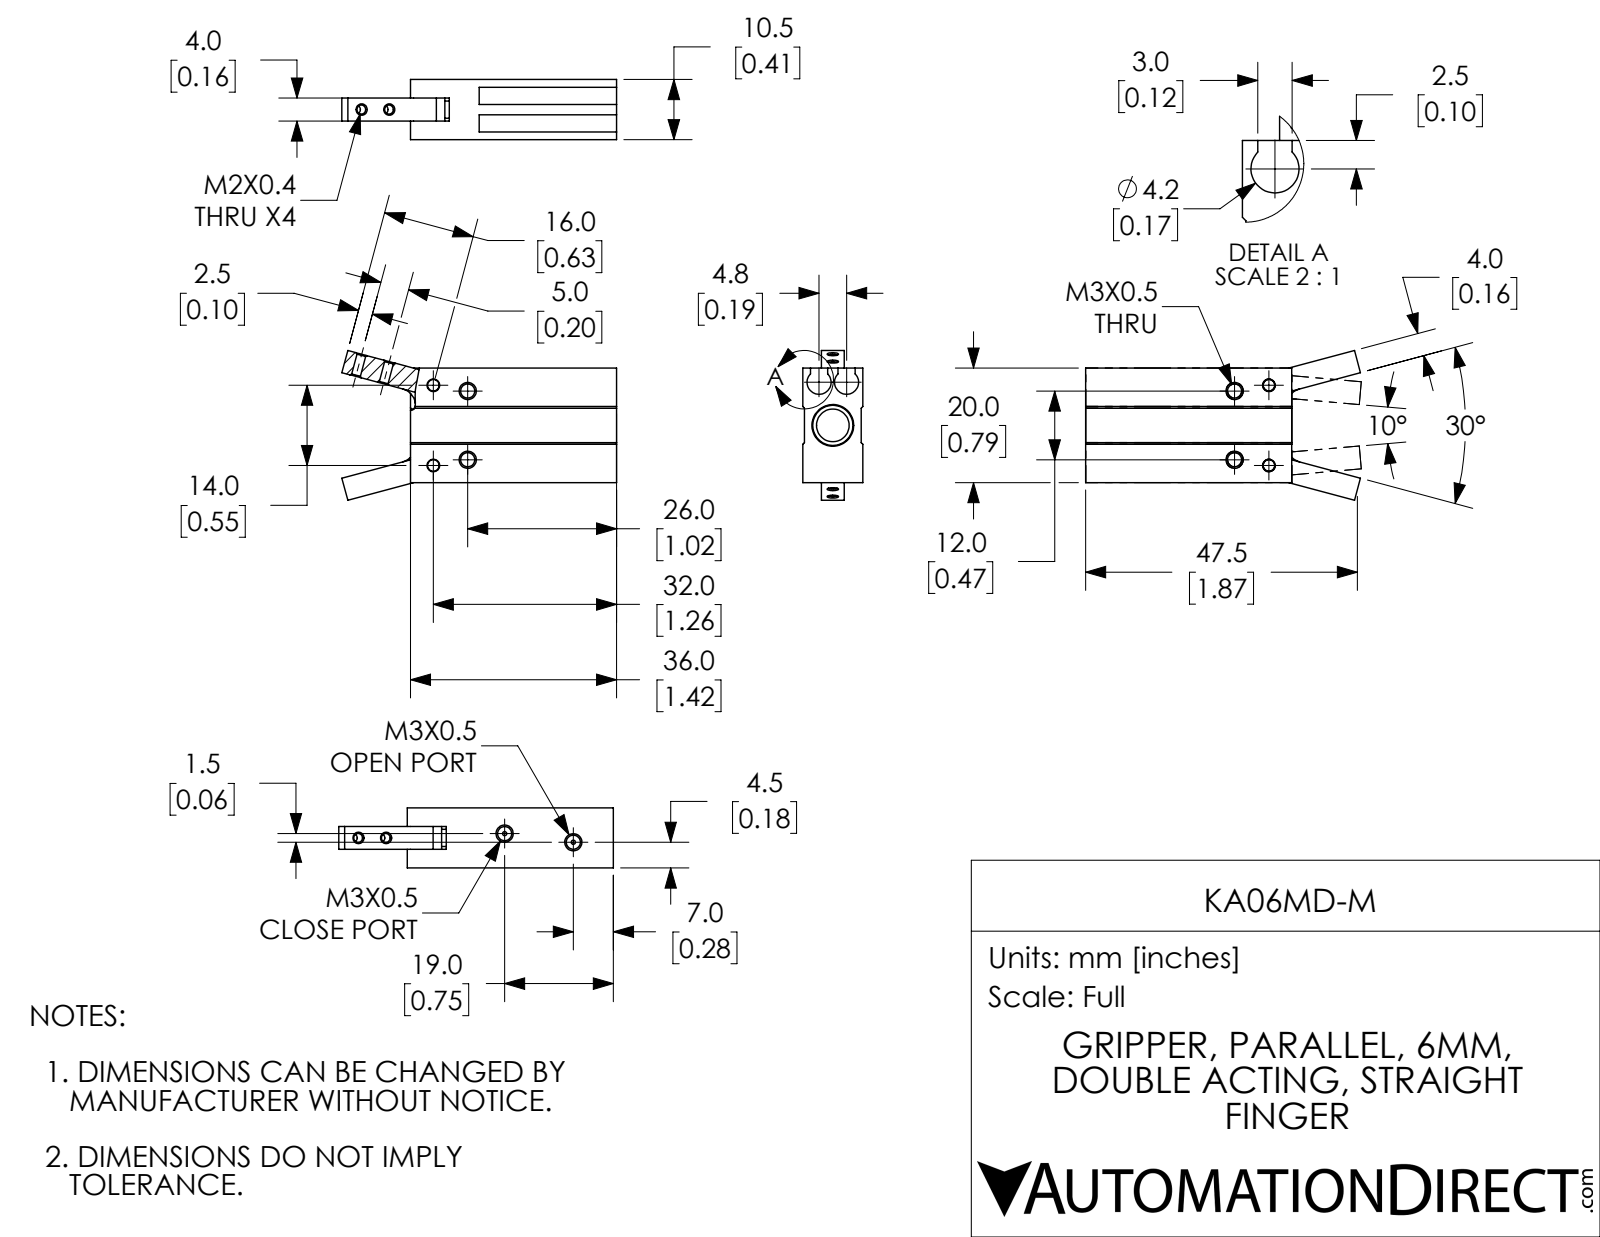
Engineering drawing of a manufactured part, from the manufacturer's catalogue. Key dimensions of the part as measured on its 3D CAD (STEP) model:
Part name (STEP PRODUCT): KA06MD-M-4; KA06MD-M; KA06MD-M-1; KA06MD-M-2 (+1 more)
STEP written by: SolidWorks 2017 (AUTOMOTIVE_DESIGN)
Units: millimetres
Bodies: 4 solids, 184 faces (66 planar, 67 cylindrical, 51 other)
Overall size (bounding box): 47.97 × 26.15 × 10.5
Volume: 6 348 mm³ · Surface area: 5 300 mm²
Round holes (diameter × count): ⌀2.46 ×3, ⌀1.57 ×2, ⌀1.57 ×2, ⌀2 ×2, ⌀1.5 ×1, ⌀2.46 ×1, ⌀3 ×1, ⌀5.7 ×1, ⌀6 ×1, ⌀7 ×1, ⌀8 ×1
Round bosses / shafts (diameter × count): ⌀5.8 ×1, ⌀4 ×1, ⌀2.8 ×1
Partial cylindrical surfaces — rounded edges, fillets, slot ends (radius × count): R2 ×2, R2.1 ×2, R3 ×2
Main face-to-face distances: 10.5, 3.25, 7.25, 10.2, 2.95, 6.95, 4, 9.9, 20, 36
Hole centre spacings: 5, 6.08, 7.25, 9.9, 14.32, 12, 12.09, 14
